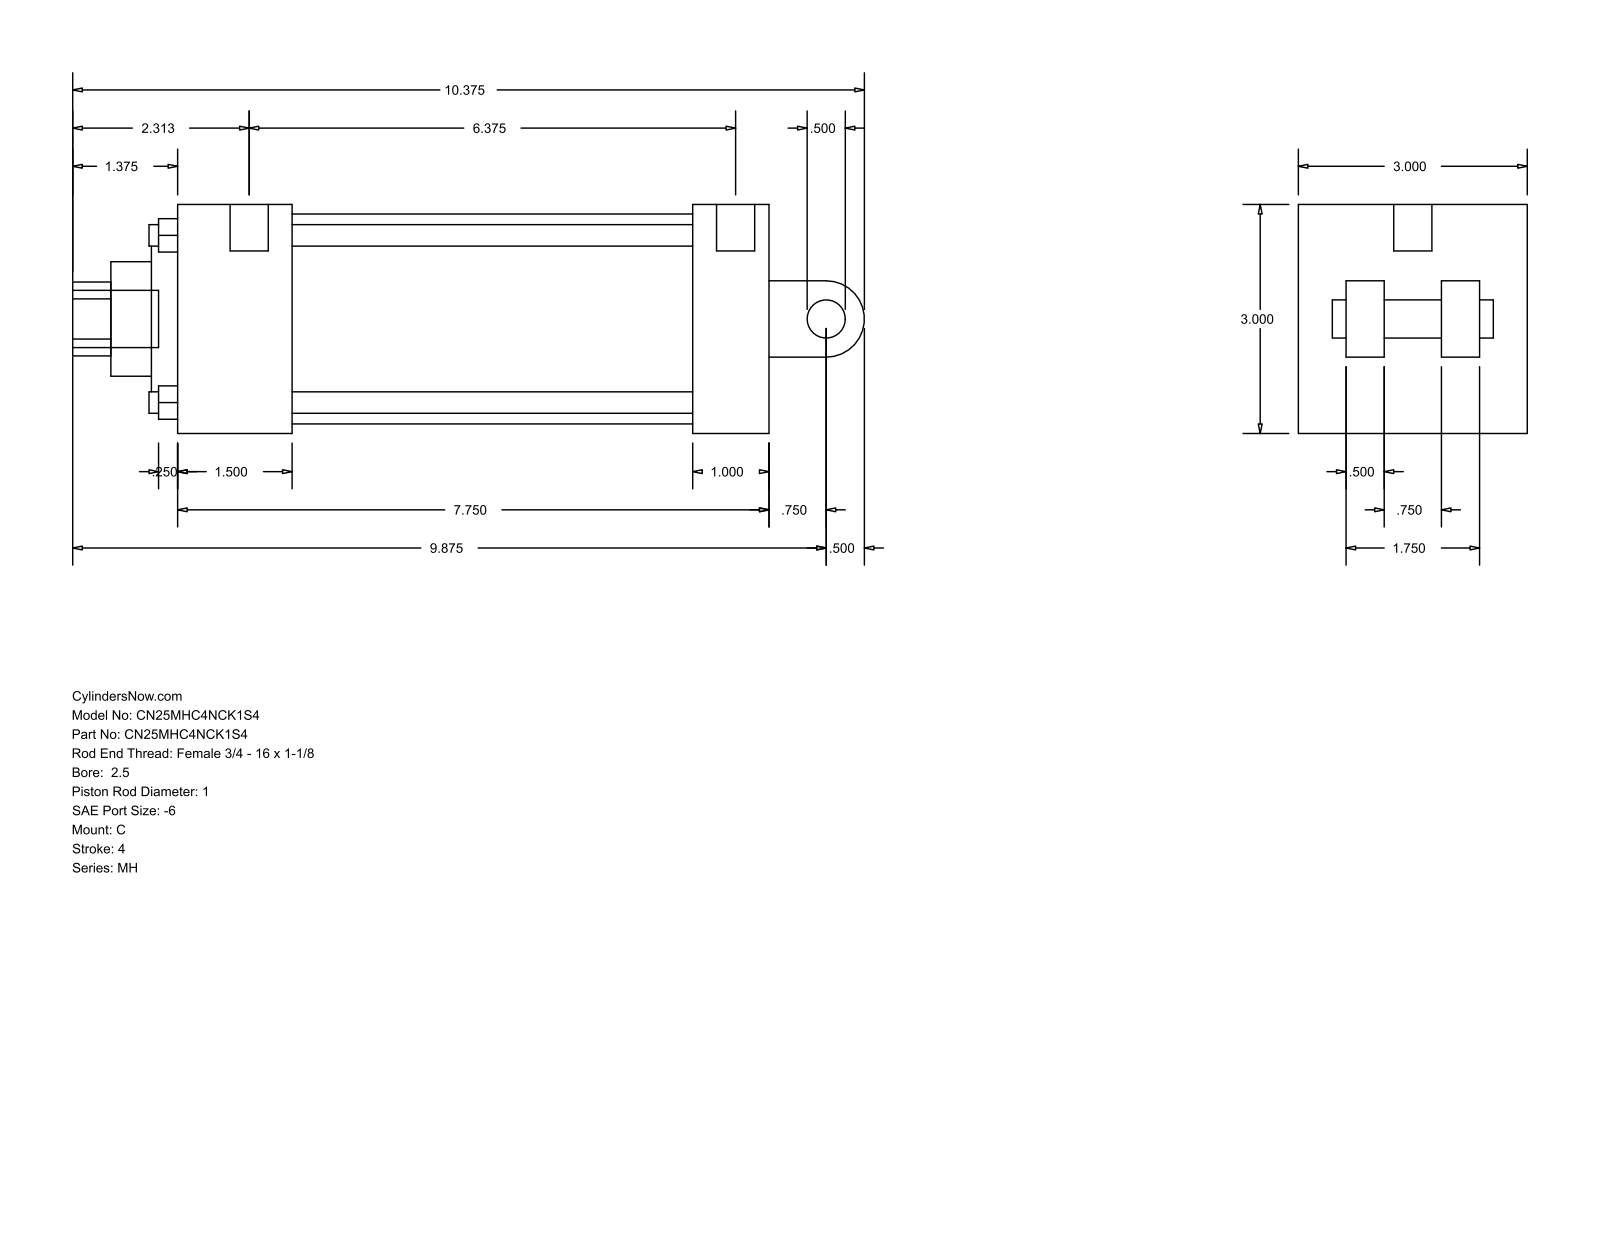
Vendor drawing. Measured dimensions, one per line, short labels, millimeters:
name: MH_C__0250_1
written by: GSSL Pune (CONFIG_CONTROL_DESIGN)
unit: mm
bodies: 0 solids, 101 faces (71 planar, 30 cylindrical, 0 other)
size: 263.52 × 76.2 × 76.2
holes: 4× ⌀7.14, 2× ⌀5.56, 1× ⌀12.7, 1× ⌀25.4, 1× ⌀38.1, 1× ⌀60.33, 1× ⌀69.85
bosses: 2× ⌀12.7, 2× ⌀5.56, 1× ⌀19.05
rounds: 1× R12.29, 1× R12.7
face distances: 76.2, 25.4, 196.86, 15.87, 60.33, 171.46, 38.11, 133.35, 158.75, 12.7
hole spacings: 39.33, 55.62, 78.66, 3.18
